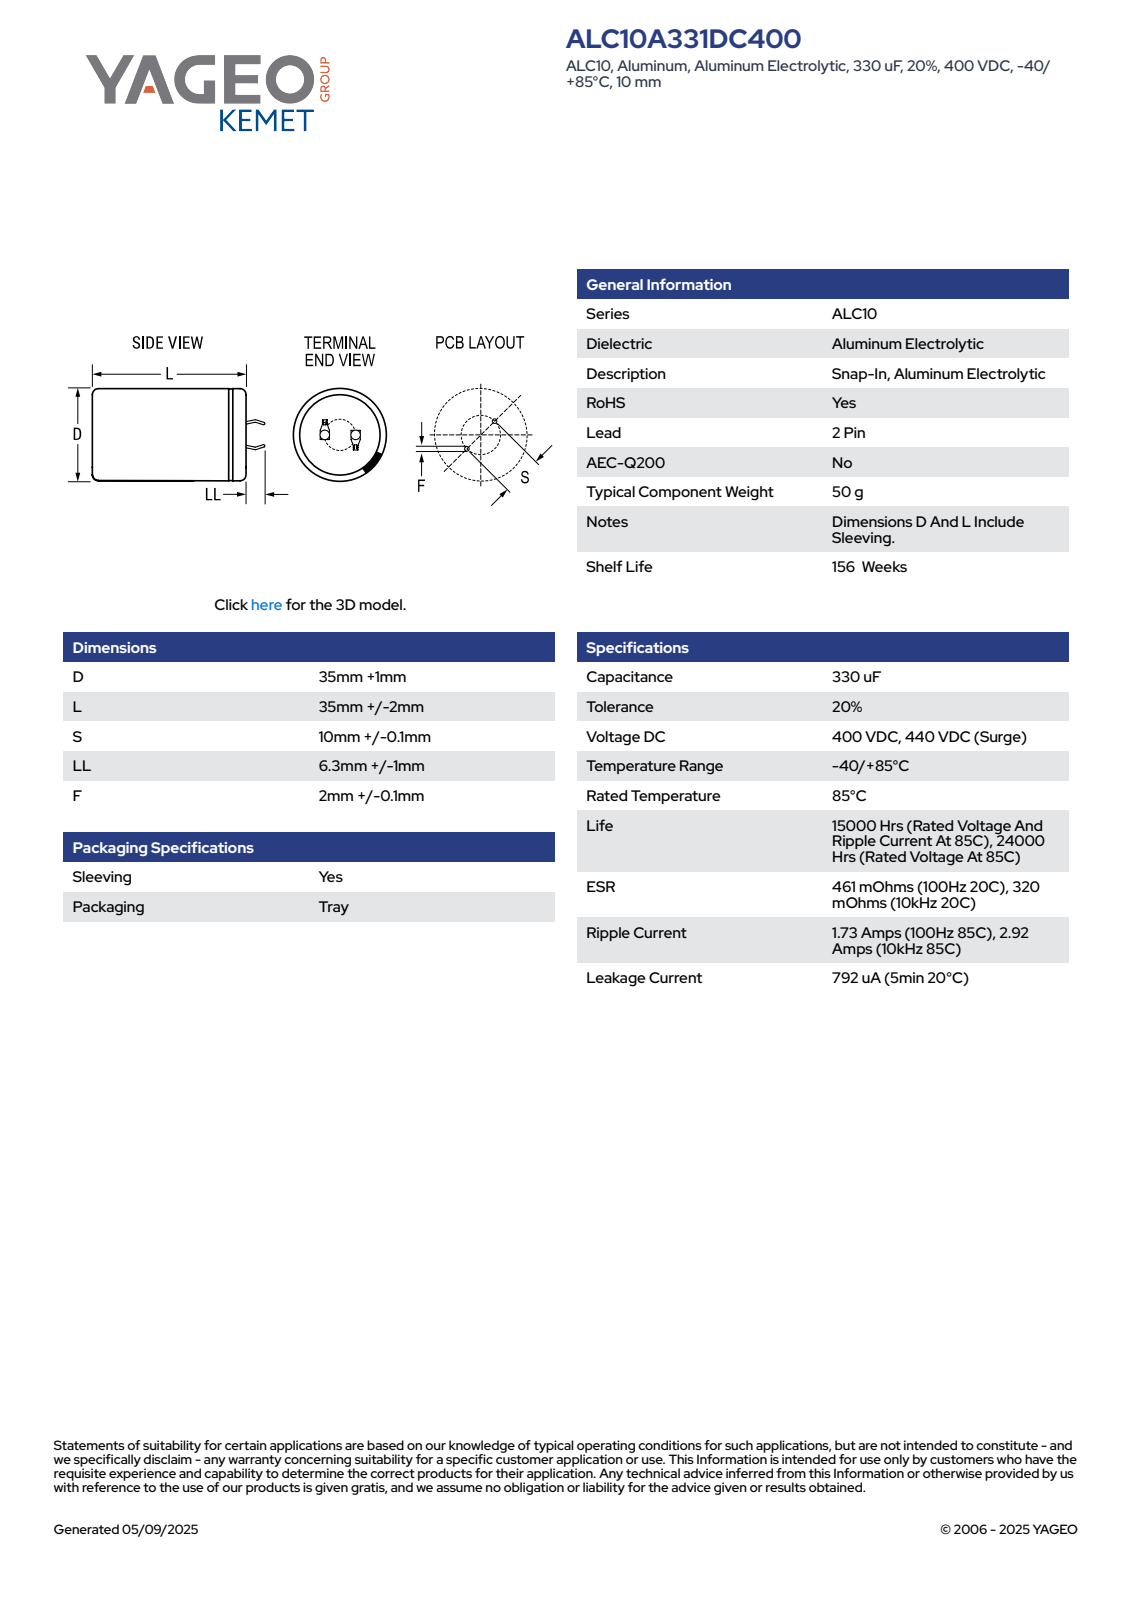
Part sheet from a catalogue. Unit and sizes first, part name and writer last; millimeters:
Units: millimetres
Overall size (bounding box): 44.29 × 36 × 36
Round holes (diameter × count): ⌀31.85 ×1
Round bosses / shafts (diameter × count): ⌀36 ×1
Partial cylindrical surfaces — rounded edges, fillets, slot ends (radius × count): R17.99 ×1
Main face-to-face distances: 36.99, 0.6, 37.49, 0.5, 7.08, 7.64, 0.75, 1.35, 7.68, 6.48
Volume: 37 133 mm³ · Surface area: 6 218 mm²
Bodies: 1 solid, 100 faces (52 planar, 9 cylindrical, 39 other)
Part name (STEP PRODUCT): CARS_K2P_35X35_D36L37S10LL7.3F2.1
STEP written by: SolidWorks 2014 (AUTOMOTIVE_DESIGN)
